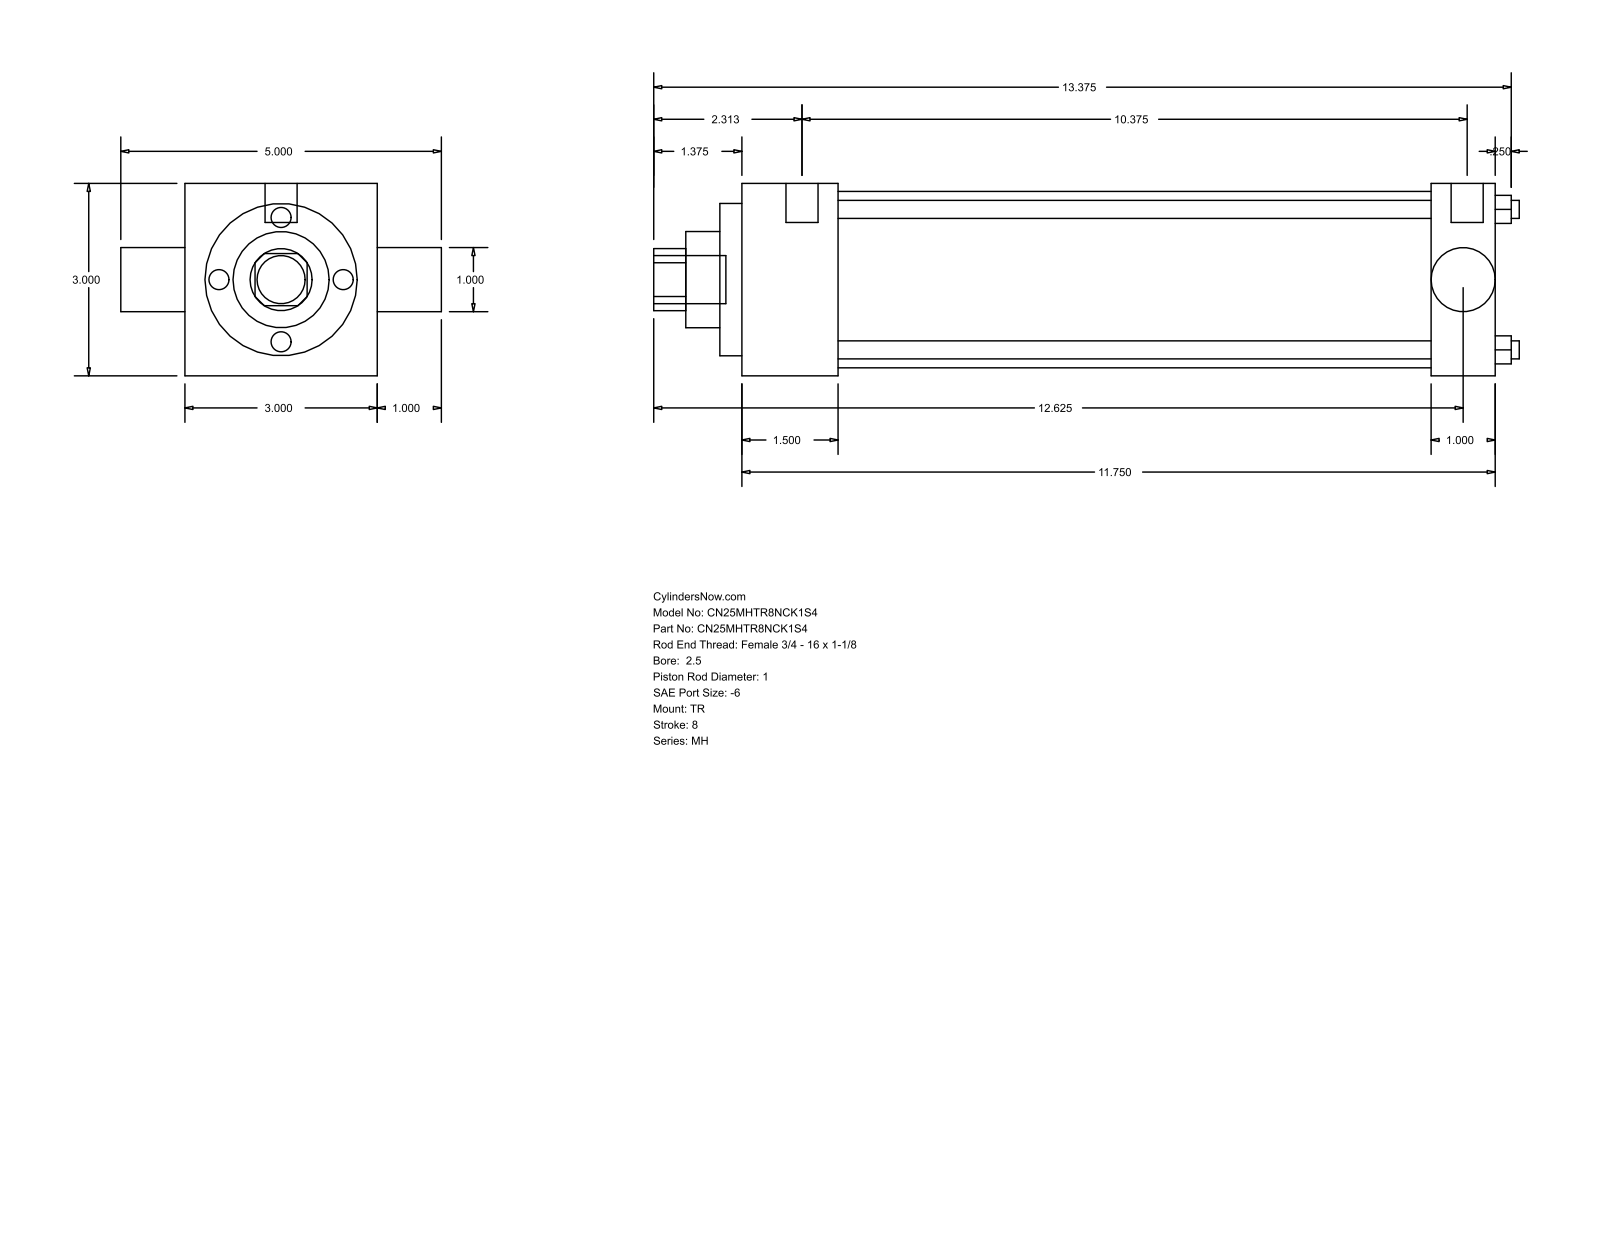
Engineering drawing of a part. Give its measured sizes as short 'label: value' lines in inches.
name: MH_TR__0250_1
written by: GSSL Pune (CONFIG_CONTROL_DESIGN)
unit: in
bodies: 0 solids, 86 faces (61 planar, 25 cylindrical, 0 other)
size: 13.5 × 5 × 3
holes: 4× ⌀0.281, 1× ⌀0.998, 1× ⌀1, 1× ⌀1.5, 1× ⌀2.375, 1× ⌀2.75
bosses: 3× ⌀0.219, 2× ⌀0.5, 1× ⌀0.75
rounds: 1× R0.484
face distances: 3, 11.75, 1, 1.5, 10.25, 10.75, 9.25, 0.344, 1.844, 11.094
hole spacings: 1.548, 2.19, 3.097
